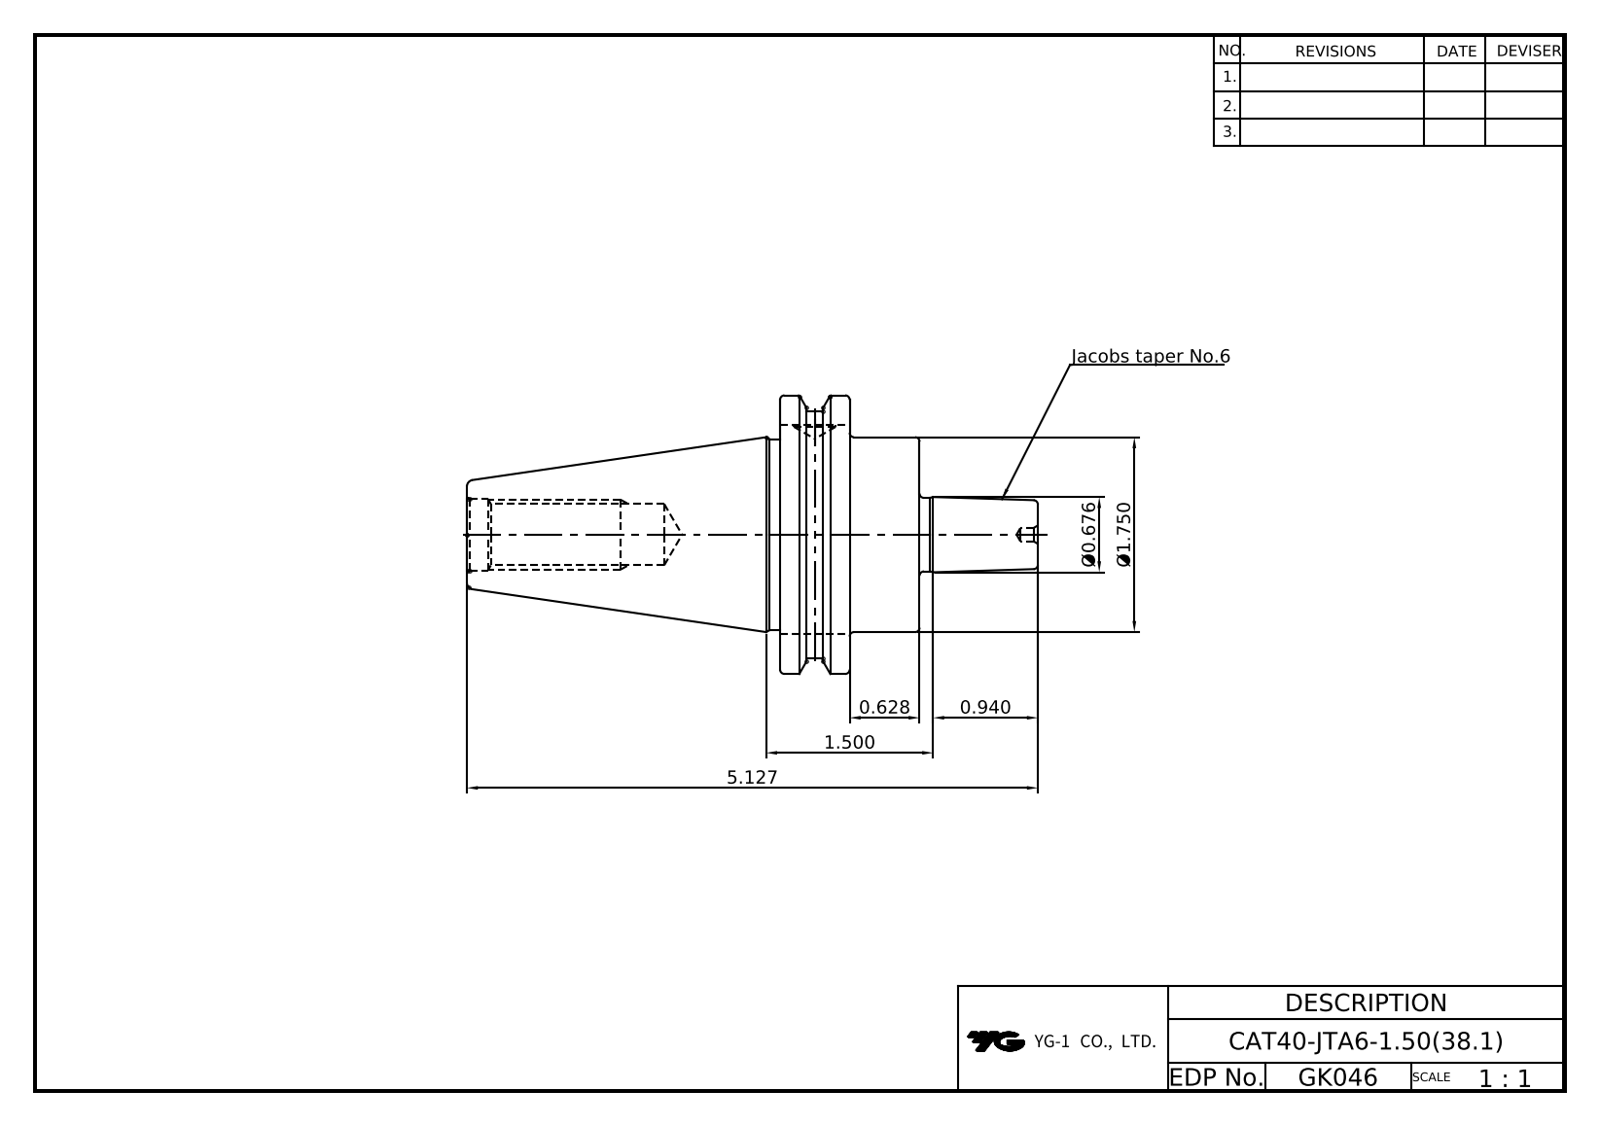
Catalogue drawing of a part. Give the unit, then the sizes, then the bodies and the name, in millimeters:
Units: millimetres
Overall size (bounding box): 130.23 × 63.5 × 61.09
Round holes (diameter × count): ⌀9.53 ×1, ⌀13.39 ×1, ⌀16.3 ×1
Round bosses / shafts (diameter × count): ⌀63.5 ×1, ⌀56.3 ×1, ⌀44.45 ×1, ⌀43.6 ×1, ⌀16.77 ×1
Main face-to-face distances: 31.83, 15.88, 15.95, 58.81, 42.93, 26.98, 47.6, 16.38, 71.42, 87.3
Volume: 137 342 mm³ · Surface area: 22 067 mm²
Bodies: 1 solid, 61 faces (28 planar, 12 cylindrical, 21 other)
Part name (STEP PRODUCT): CAT40-JTA6-1.50(20231109)
STEP written by: Autodesk Inventor 2024 (AUTOMOTIVE_DESIGN)
